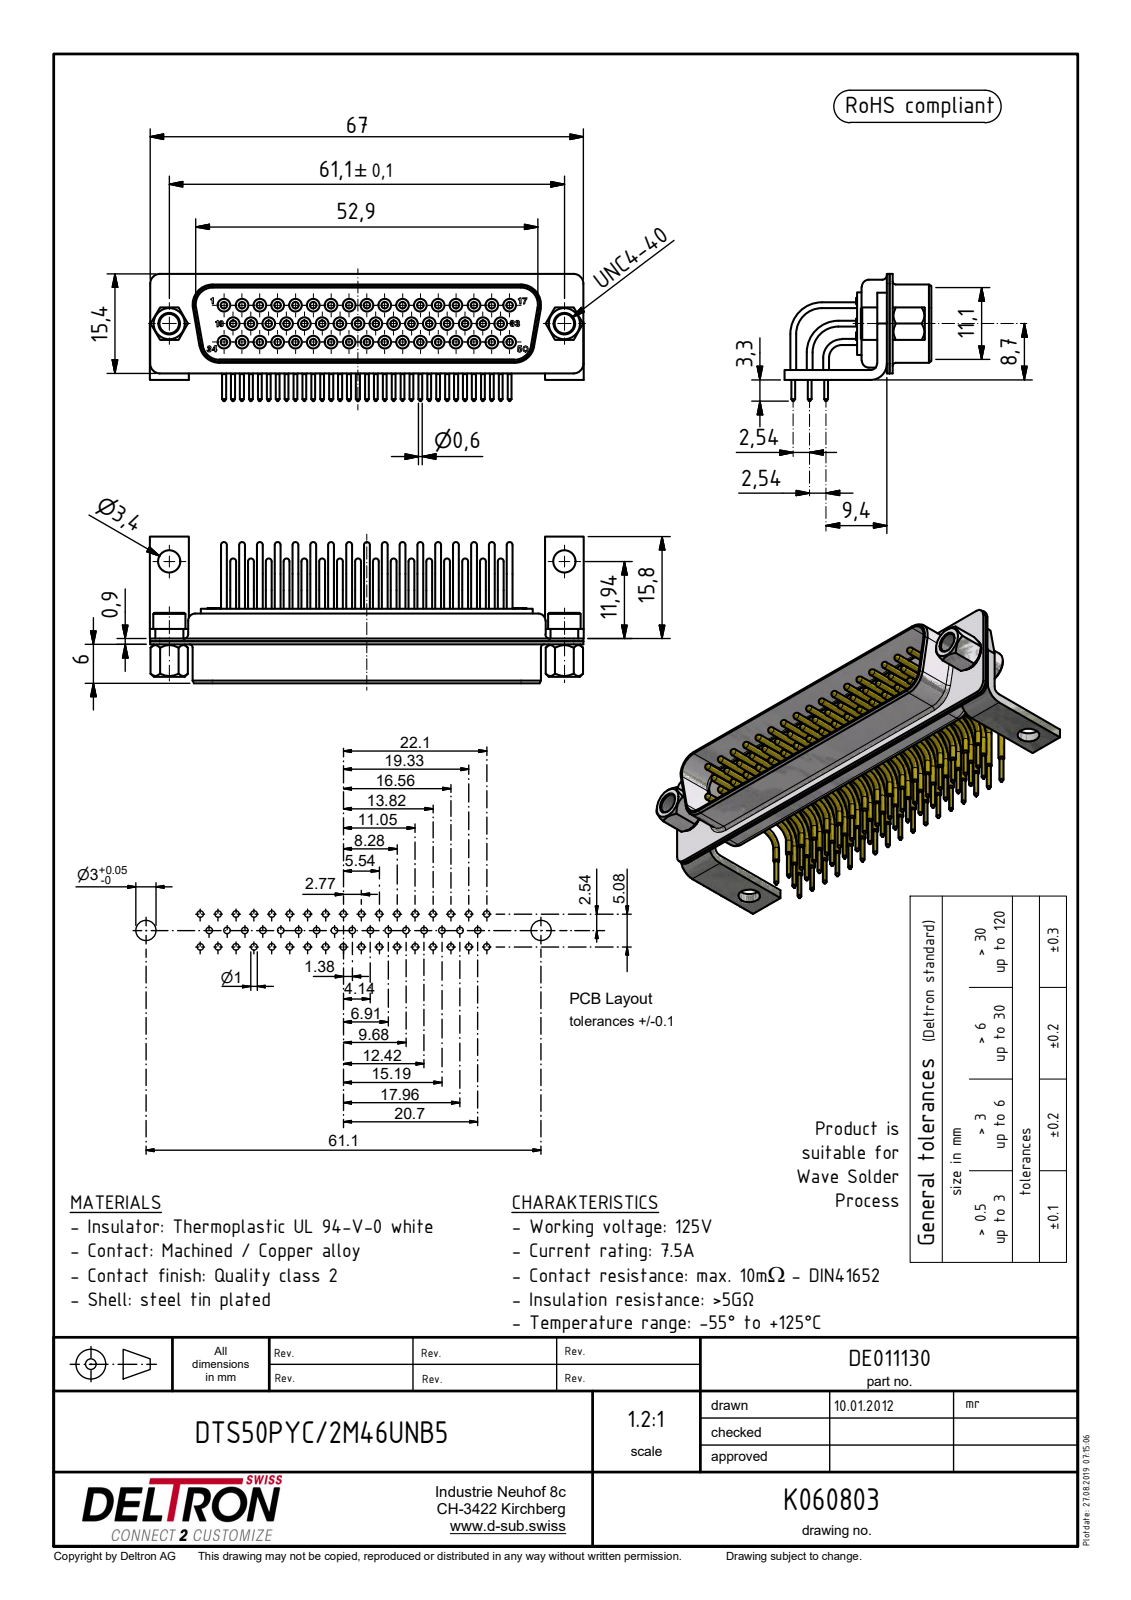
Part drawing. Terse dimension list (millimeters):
name: N00789_BG; R+B00082_BG; R+B00914_BG; R+B00913_BG (+6 more)
written by: Autodesk Inventor 2015 (AUTOMOTIVE_DESIGN)
unit: mm
bodies: 59 solids, 7228 faces (4240 planar, 2506 cylindrical, 482 other)
size: 67.1 × 22.7 × 19.72
volume: 5 118 mm³; area: 14 000 mm²
holes: 50× ⌀1.92, 50× ⌀2.3, 2× ⌀0.24, 2× ⌀0.28, 2× ⌀0.34, 2× ⌀3, 2× ⌀3.2, 2× ⌀3.4, 2× ⌀4.05, 2× ⌀4.06
bosses: 100× ⌀0.9, 50× ⌀1.96, 50× ⌀1.94, 50× ⌀1.6, 50× ⌀1.6, 50× ⌀1, 50× ⌀0.6, 2× ⌀5
rounds: 50× R1.07, 12× R2, 9× R1, 8× R0.7, 8× R1.1, 6× R0.25, 4× R0.5, 4× R1.2
face distances: 0.5, 0.4, 0.9, 11.6, 5, 0.75, 12.35, 2.4, 1.65, 4.2
hole spacings: 2.76, 5.52, 3.16, 8.28, 5.02, 7.46, 11.04, 10.07
